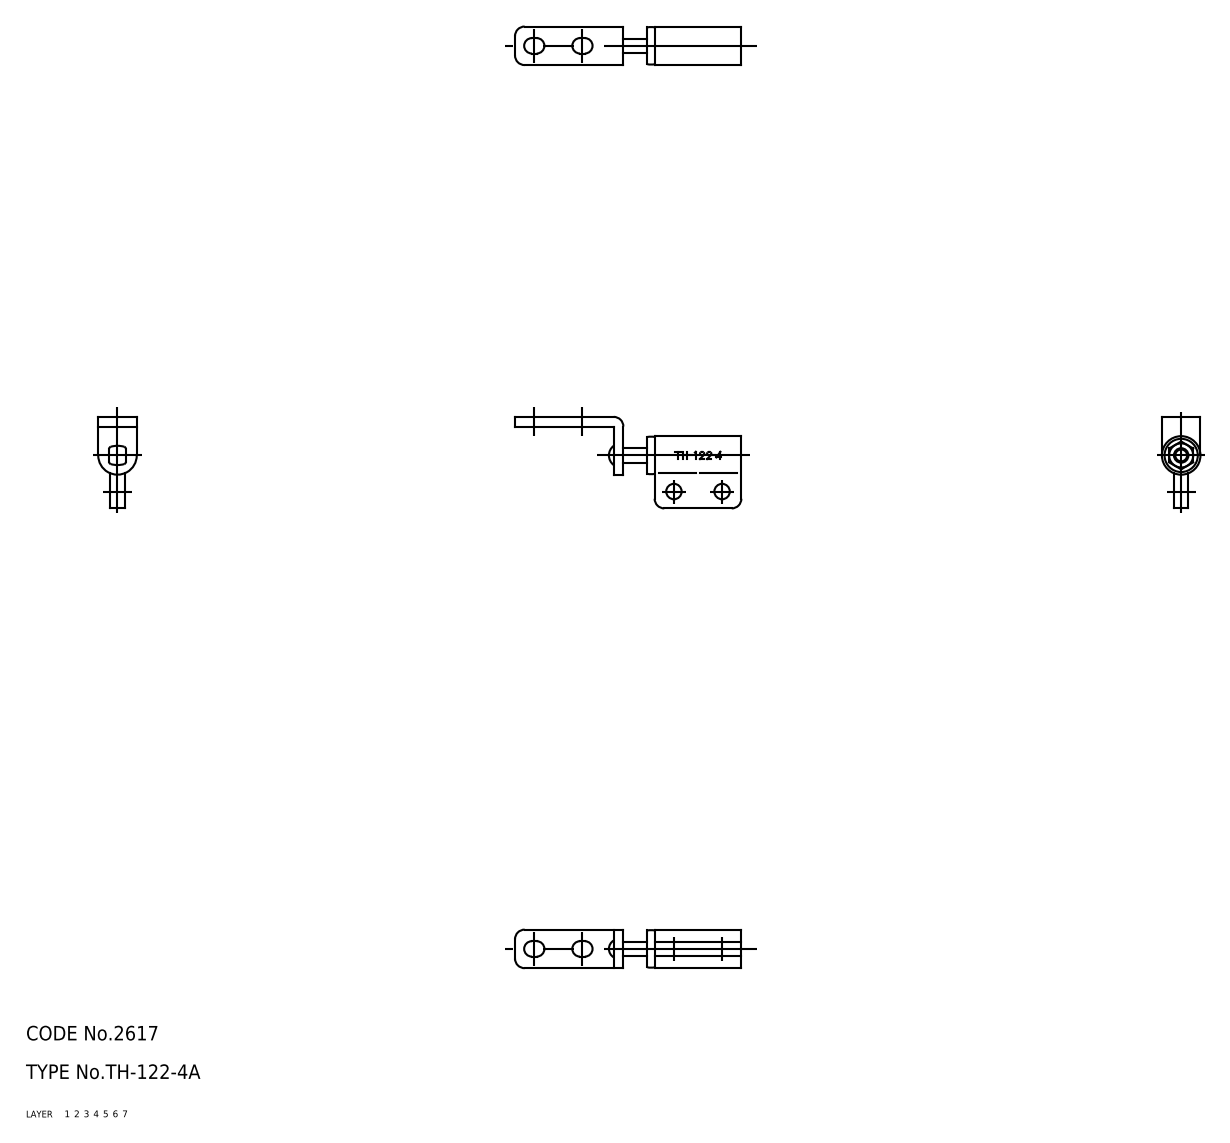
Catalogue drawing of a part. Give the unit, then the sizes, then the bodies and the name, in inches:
Units: inches
Overall size (bounding box): 1.85 × 0.748 × 0.315
Volume: 0.089 in³ · Surface area: 4.58 in²
Bodies: 6 solids, 96 faces (0 planar, 0 cylindrical, 96 other)
Part name (STEP PRODUCT): washer; socket; shaft; nut (+3 more)
STEP written by: CADfix (AUTOMOTIVE_DESIGN)
